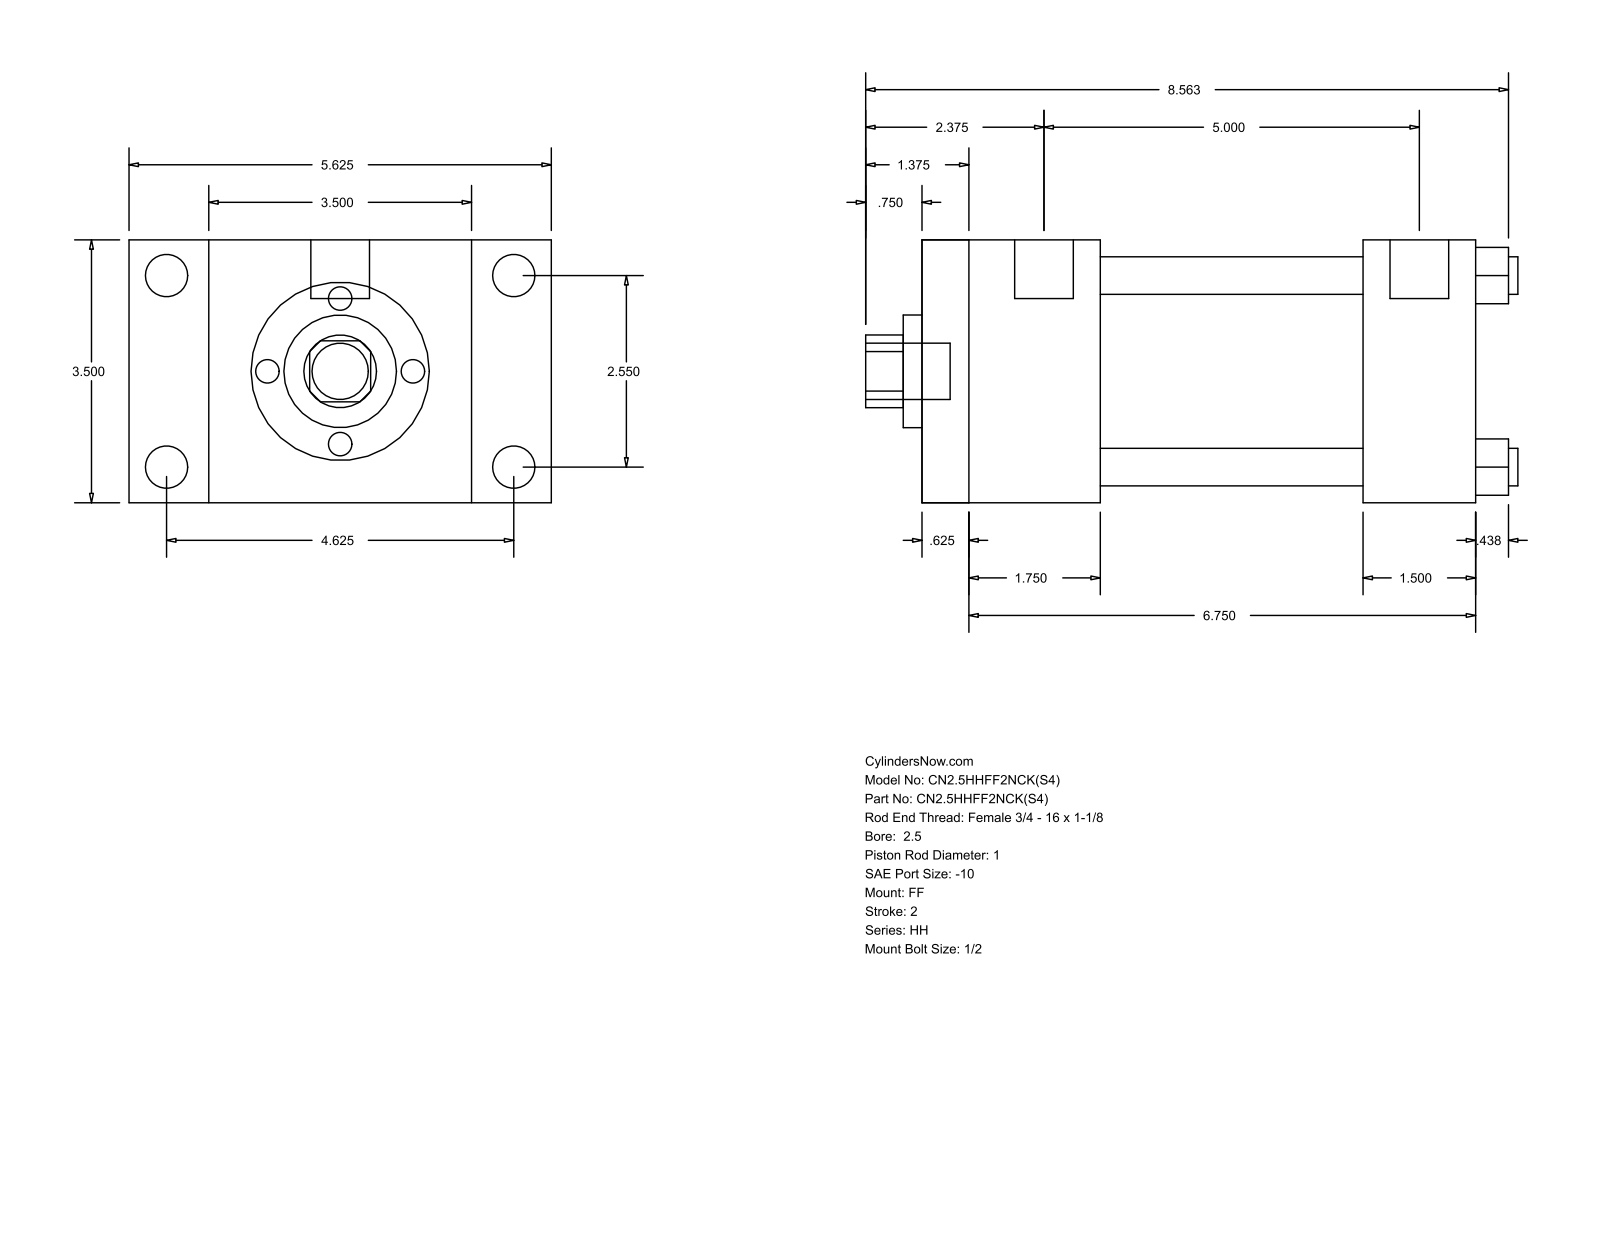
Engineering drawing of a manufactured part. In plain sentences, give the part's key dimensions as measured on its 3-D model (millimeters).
The part is named "HH_FF__0250_1". Its 3-D file was written by "GSSL Pune (CONFIG_CONTROL_DESIGN)". It is 0 solids with 92 faces: 64 planar, 28 cylindrical and 0 other. Overall it measures 220.66 by 142.88 by 88.9 millimeters. Round holes: 4 of diameter 12.7, 1 of diameter 25.4, 1 of diameter 38.1, 1 of diameter 73.03. Round bosses or shafts: 4 of diameter 14.3, 4 of diameter 5.56, 2 of diameter 19.84, 1 of diameter 19.05. Partial cylindrical surfaces (rounded edges, fillets, slot ends): 1 of radius 12.29. The main face-to-face distances are 88.9, 187.33, 15.87, 171.46, 60.33, 44.46, 127, 149.23, 133.36, 38.1. The hole center spacings are 45.79, 64.76, 91.58.
